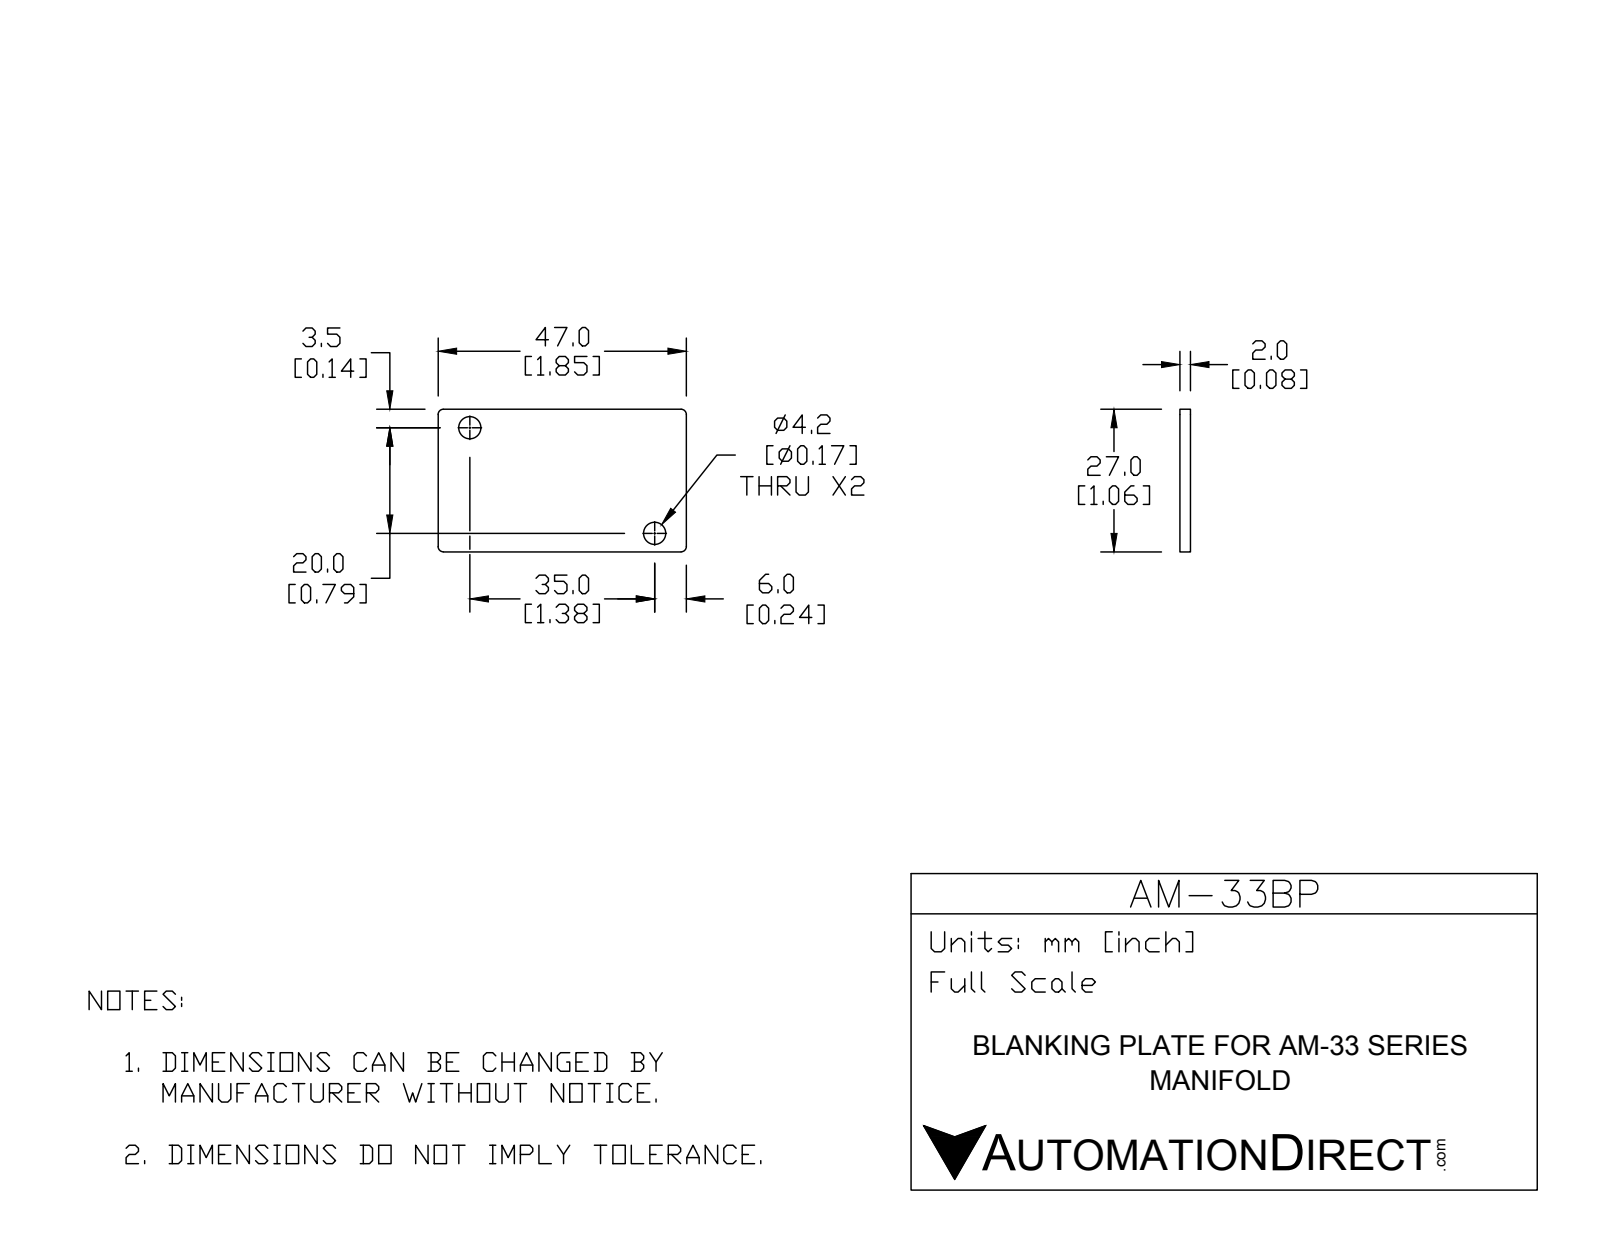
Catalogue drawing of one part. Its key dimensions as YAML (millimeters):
part_name: "AM-33BP"
step_written_by: "SolidWorks 2016 (AUTOMOTIVE_DESIGN)"
units: millimeters
bodies: {solids: 1, faces: 14, planar: 6, cylindrical: 8, other: 0}
overall_size: [47, 27, 2]
volume: 2481
surface_area: 2826
round_holes:
  - {diameter: 4.2, count: 2}
partial_cylinders:
  - {radius: 1, count: 4}
face_to_face_distances: [2, 27, 47]
hole_center_spacings: [40.31]
